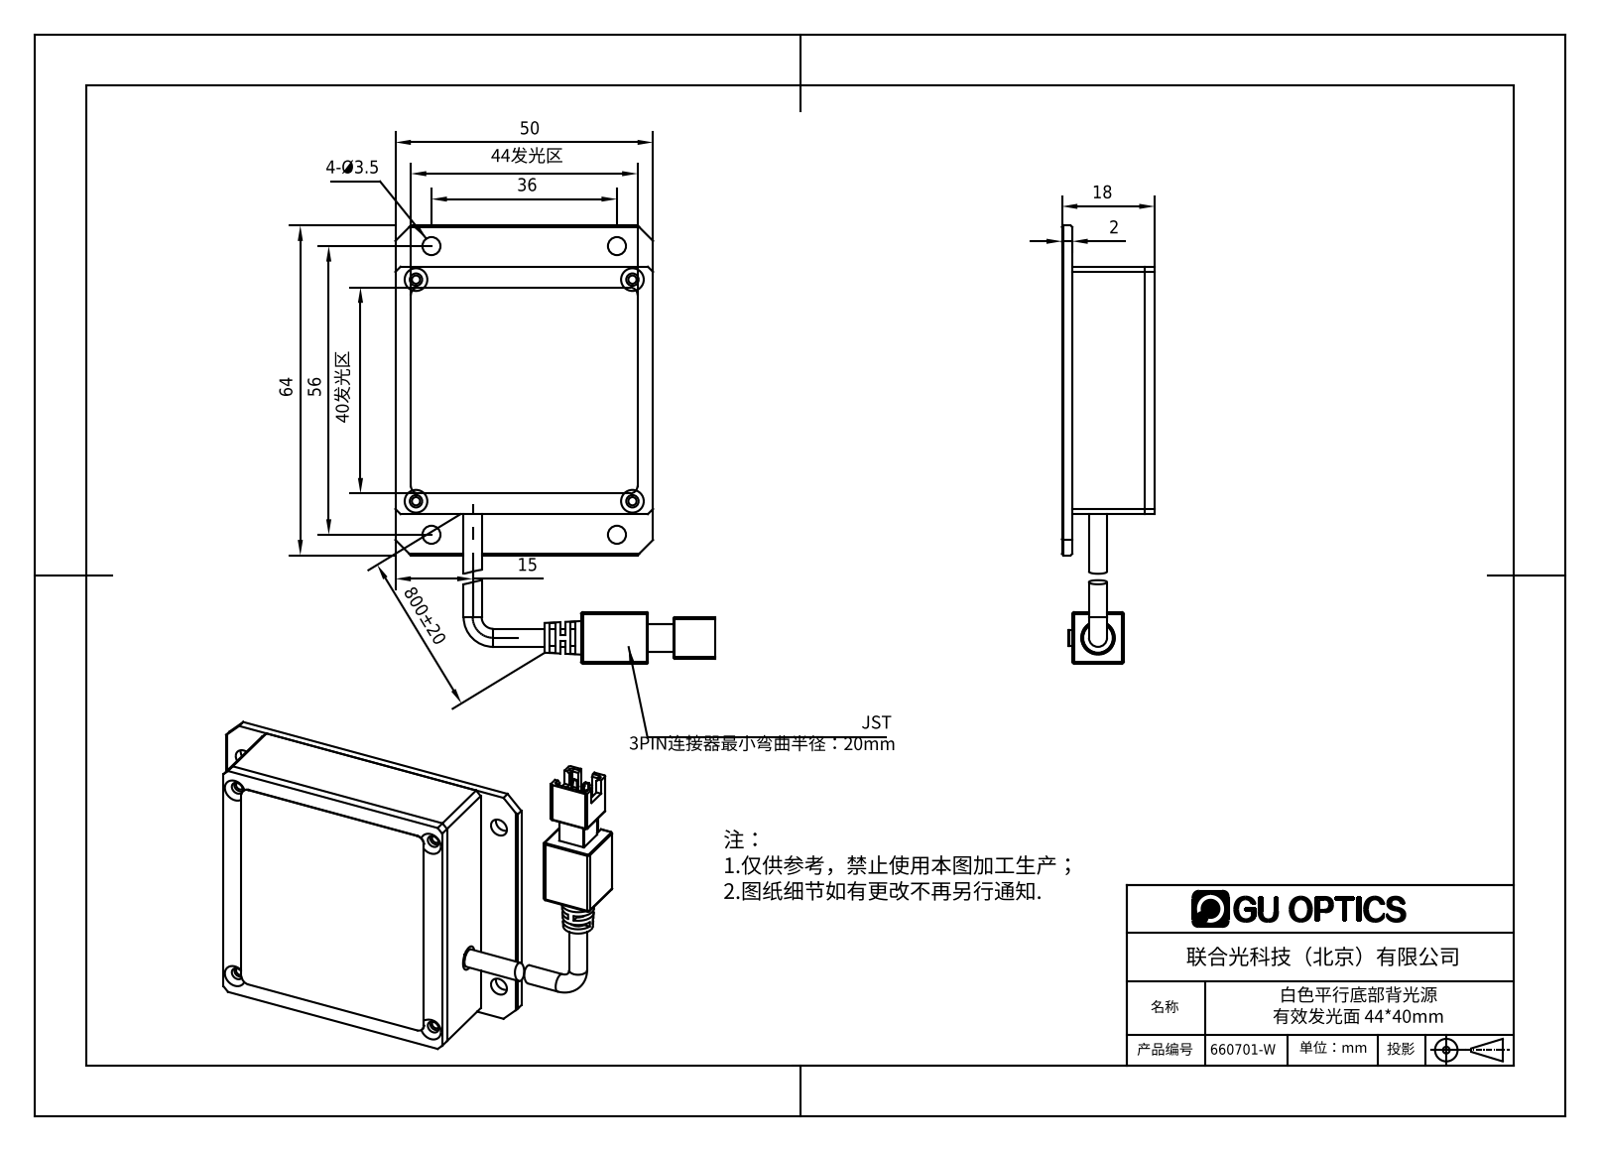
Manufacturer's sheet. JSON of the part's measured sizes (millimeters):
{"part_name": "660701-W", "step_written_by": "SolidWorks 2016 (AUTOMOTIVE_DESIGN)", "units": "millimeters", "bodies": {"solids": 7, "faces": 477, "planar": 240, "cylindrical": 118, "other": 119}, "overall_size": [85, 62, 18.1], "volume_mm3": 23667, "surface_area_mm2": 28120, "round_holes": [[1.6, 8], [2.4, 8], [3.5, 4]], "round_bosses_or_shafts": [[3.5, 2]], "partial_cylinders_radius": [[0.1, 15], [0.2, 13], [0.4, 12], [1.5, 6], [1, 4], [0.3, 1], [0.68, 1], [1.4, 1]], "face_to_face_distances": [16, 2, 3, 14, 18, 1, 13, 15, 2.1, 15.1], "hole_center_spacings": [1, 6.26, 7.16, 39.39, 39.54, 42, 42.01, 44]}
